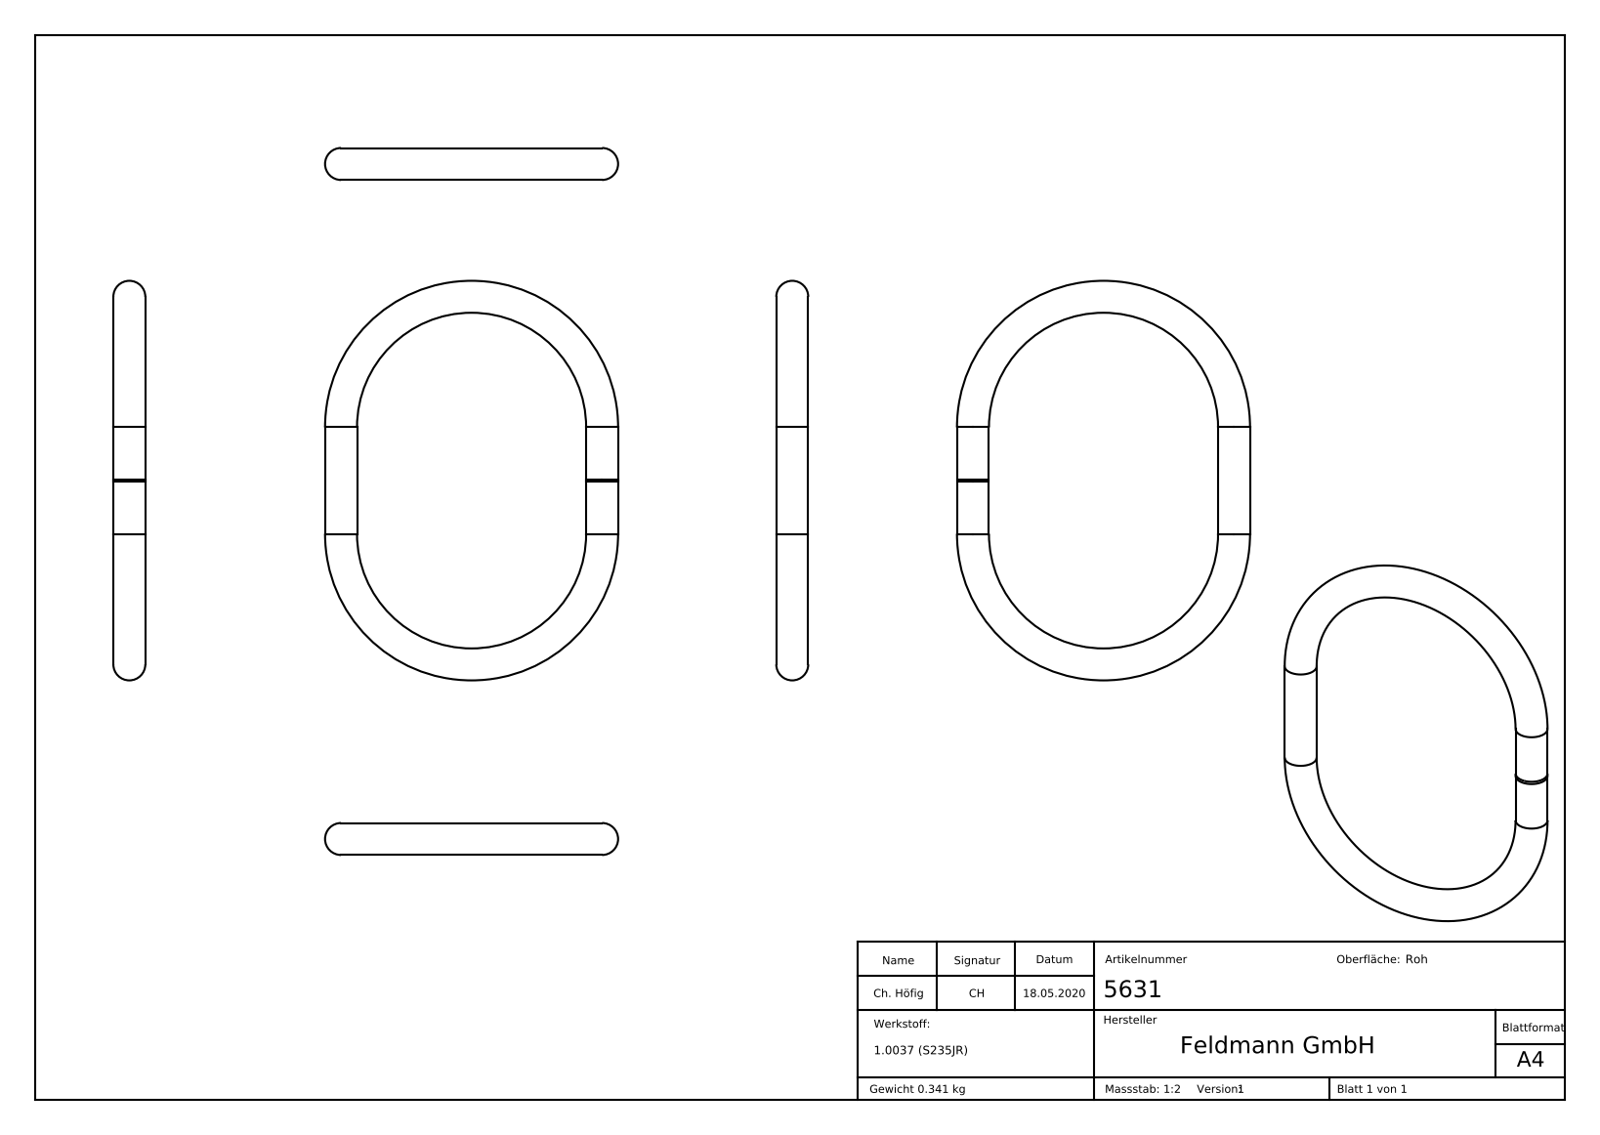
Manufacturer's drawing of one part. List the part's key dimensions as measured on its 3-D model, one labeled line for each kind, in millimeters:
Part name (STEP PRODUCT): 5631
STEP written by: SolidWorks 2015 (CONFIG_CONTROL_DESIGN)
Units: millimetres
Bodies: 1 solid, 174 faces (90 planar, 3 cylindrical, 81 other)
Overall size (bounding box): 150 × 110 × 12
Volume: 43 755 mm³ · Surface area: 14 815 mm²
Round bosses / shafts (diameter × count): ⌀12 ×2
Main face-to-face distances: 1, 1.1, 1.78, 0.83, 0.99, 2.25, 0.67, 1.21, 3.46, 0.44
